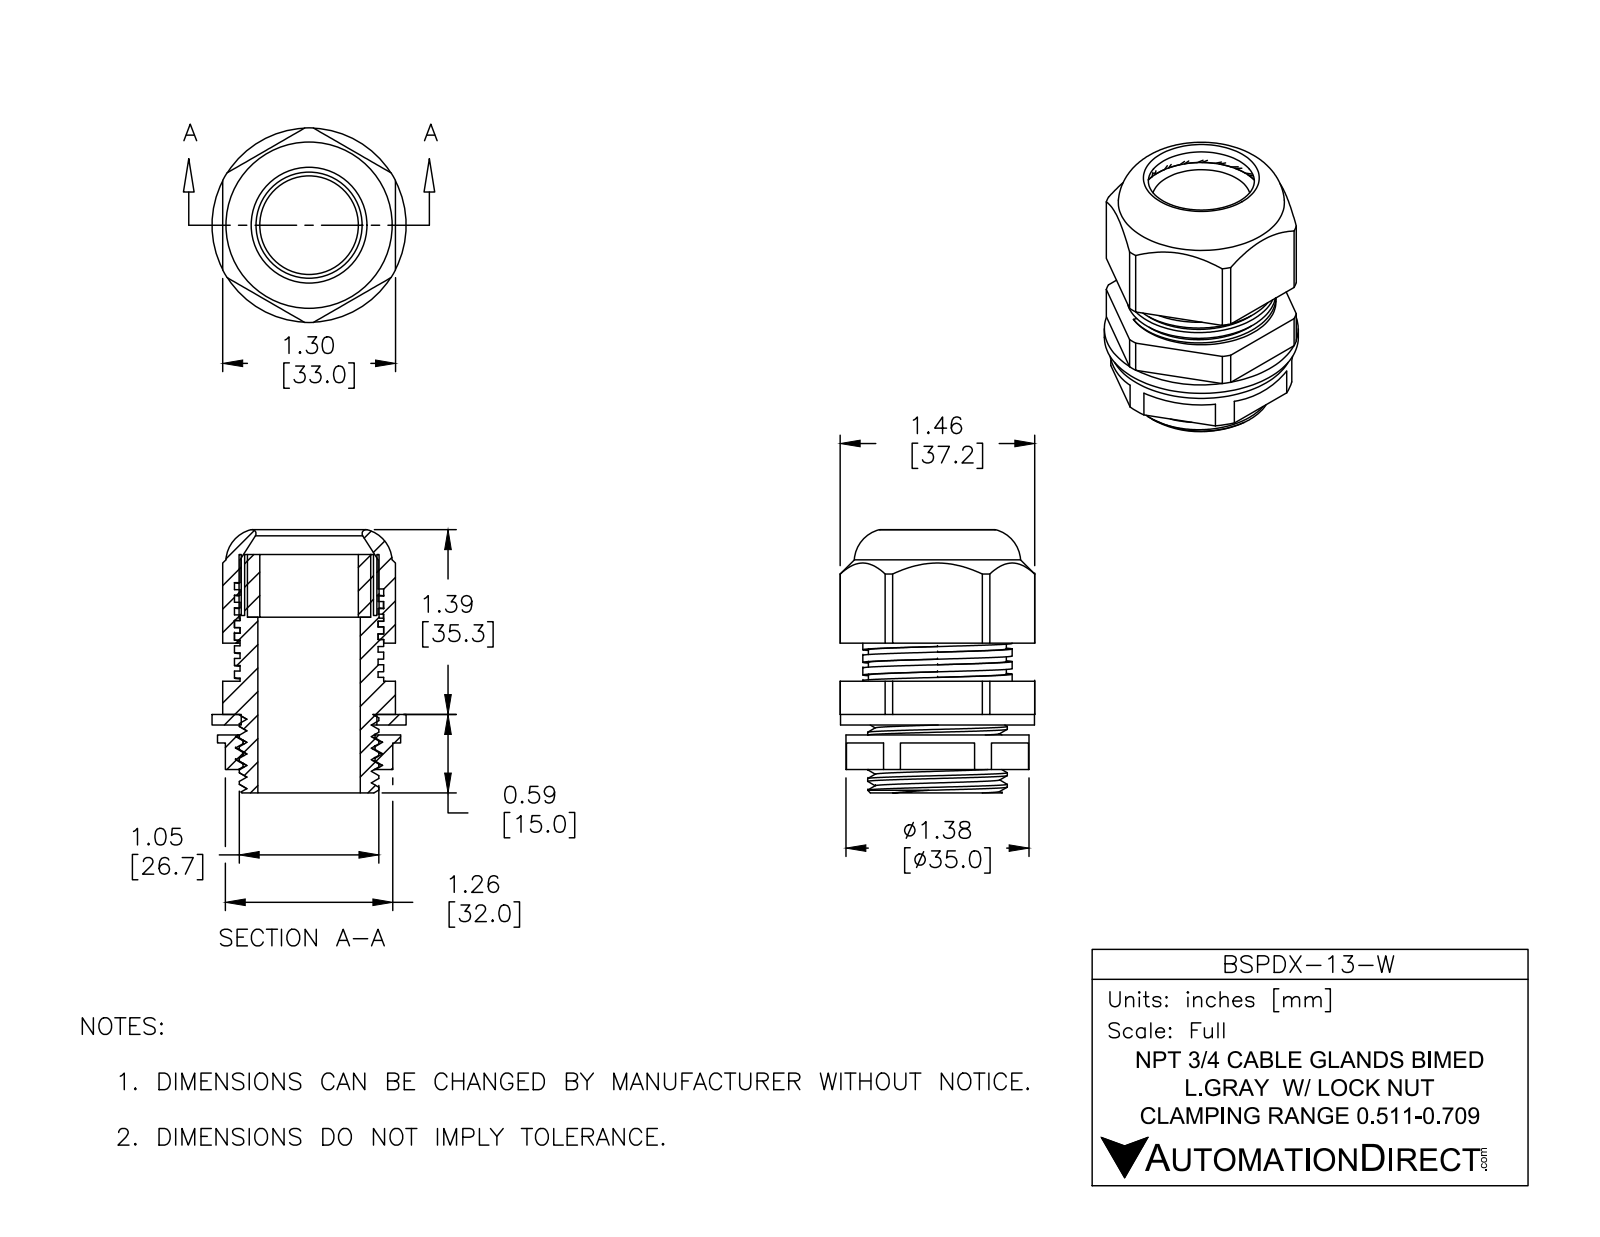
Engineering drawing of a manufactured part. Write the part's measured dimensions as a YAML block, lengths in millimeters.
part_name: "BSPDX-13-W"
step_written_by: "SolidWorks 2015 (CONFIG_CONTROL_DESIGN)"
units: millimeters
bodies: {solids: 5, faces: 224, planar: 126, cylindrical: 74, other: 24}
overall_size: [50.3, 37.2, 37.1]
volume: 24330
surface_area: 22560
round_holes:
  - {diameter: 18.8, count: 1}
  - {diameter: 19.6, count: 1}
  - {diameter: 23.5, count: 1}
  - {diameter: 25.2, count: 1}
  - {diameter: 25.9, count: 1}
  - {diameter: 26.4, count: 1}
round_bosses_or_shafts:
  - {diameter: 37.1, count: 1}
  - {diameter: 35, count: 1}
  - {diameter: 28.5, count: 1}
  - {diameter: 26.7, count: 1}
  - {diameter: 26.7, count: 1}
partial_cylinders:
  - {radius: 18.6, count: 1}
face_to_face_distances: [33, 0.5, 2, 0.5, 32.5, 1.9, 3.9, 19.9, 10.3, 8.4]
